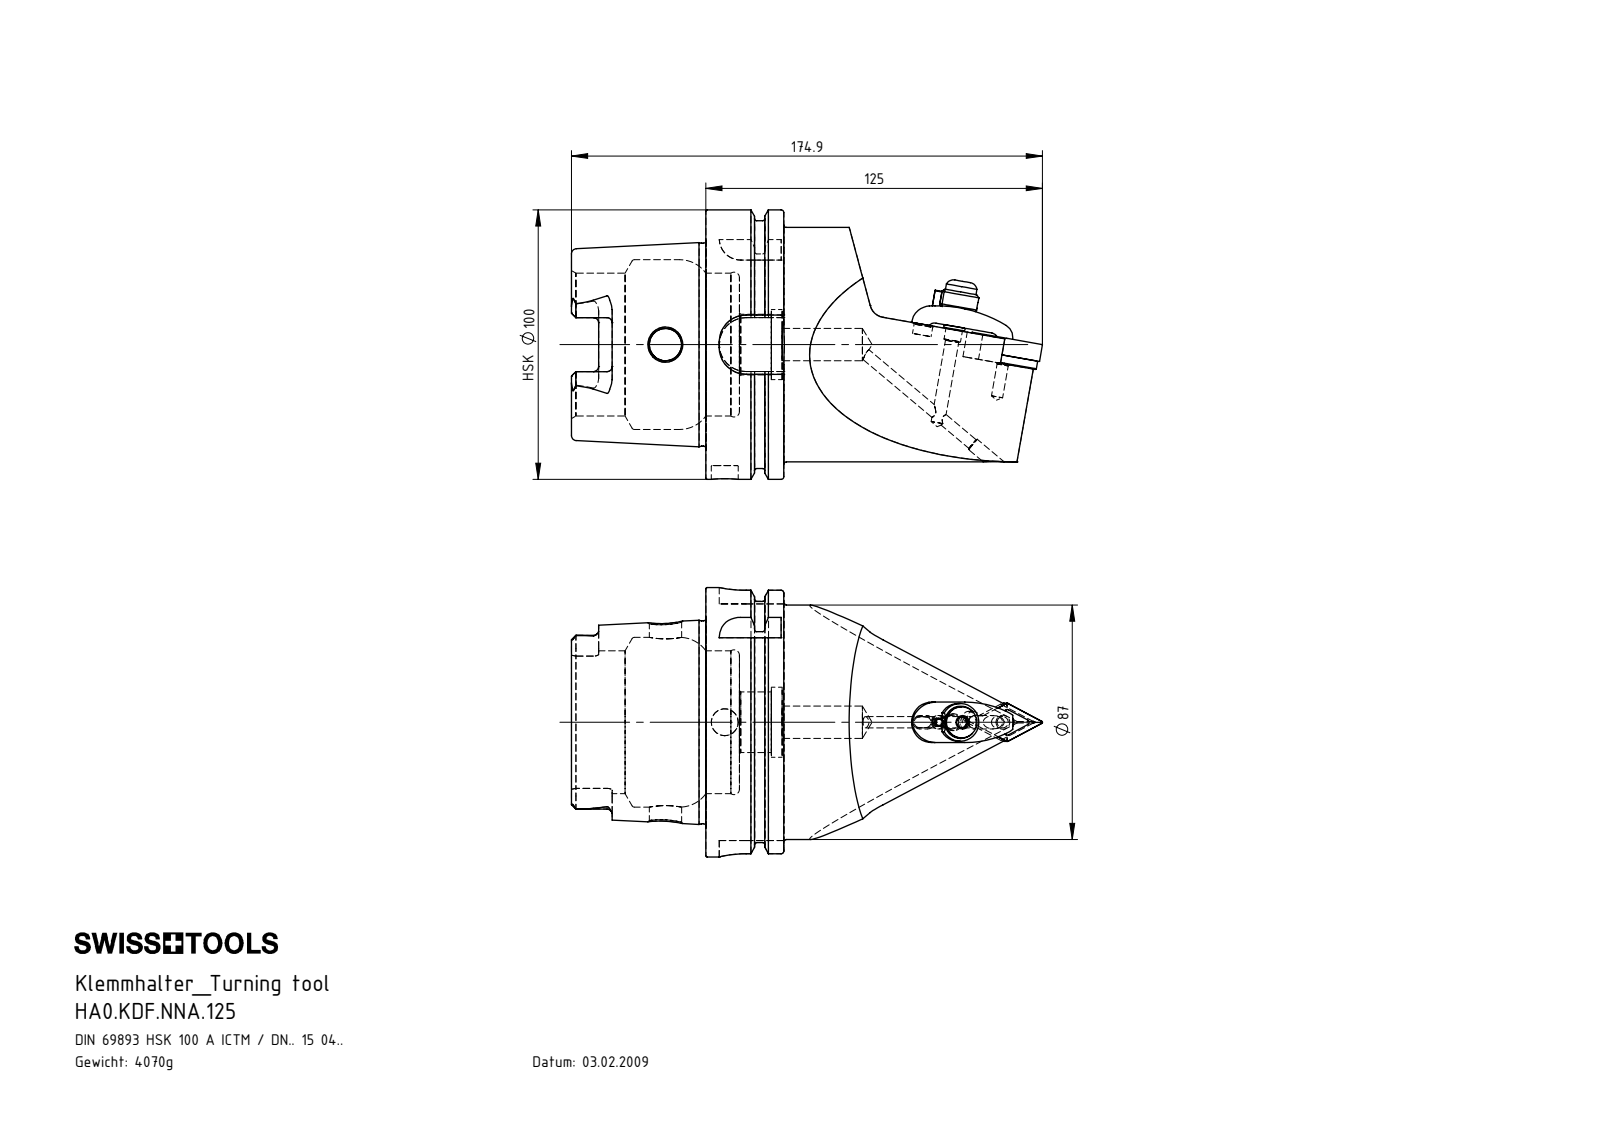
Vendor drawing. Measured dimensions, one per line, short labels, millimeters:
name: WCC-ER3.102.029_C; KVT_MB_600_050; WCC-ER5.102.005_A; WDF-ER2.101.003_A (+7 more)
written by: SolidWorks 2017 (AUTOMOTIVE_DESIGN)
unit: mm
bodies: 11 solids, 467 faces (119 planar, 155 cylindrical, 193 other)
size: 174.9 × 100 × 100
volume: 519 045 mm³; area: 72 271 mm²
holes: 3× ⌀2, 2× ⌀5, 2× ⌀7, 2× ⌀12, 1× ⌀2.4, 1× ⌀3, 1× ⌀4, 1× ⌀4.2, 1× ⌀5.16, 1× ⌀6, 1× ⌀6.2, 1× ⌀6.5
bosses: 2× ⌀5, 2× ⌀3, 1× ⌀100, 1× ⌀91.95, 1× ⌀87, 1× ⌀75.26, 1× ⌀14, 1× ⌀11.5
rounds: 6× R0.39, 6× R0.4, 6× R0.69, 6× R1.9, 3× R1.5, 3× R10, 2× R2, 2× R3
face distances: 12.45, 16.5, 28.95, 49.9, 62.35, 78.85, 87.8, 78.2, 28.3, 15.85
hole spacings: 28, 7.99, 8, 20, 20.01, 8.19, 8.2, 19.8
